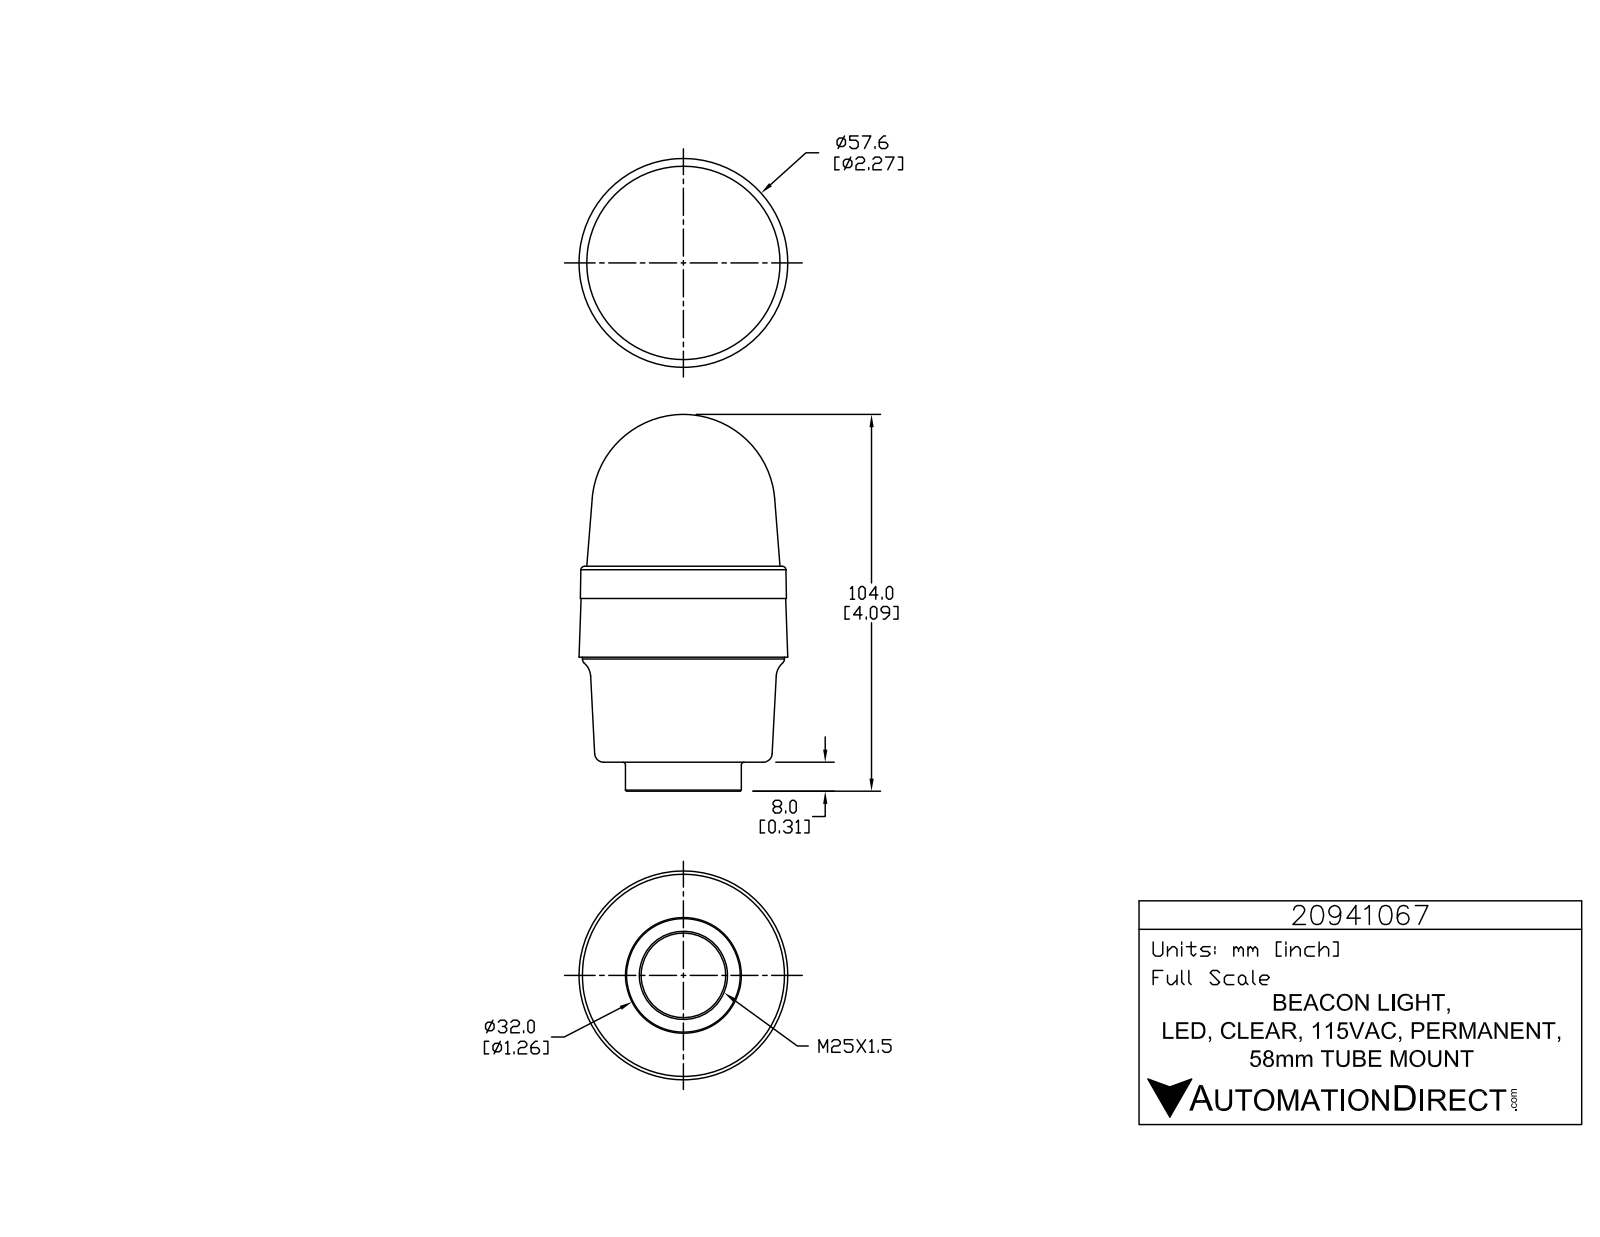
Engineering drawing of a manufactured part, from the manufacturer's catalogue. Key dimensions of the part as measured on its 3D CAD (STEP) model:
Part name (STEP PRODUCT): 20941067
STEP written by: SolidWorks 2015 (AUTOMOTIVE_DESIGN)
Units: inches
Bodies: 1 solid, 791 faces (525 planar, 168 cylindrical, 98 other)
Overall size (bounding box): 4.051 × 2.269 × 2.269
Volume: 11.72 in³ · Surface area: 29.93 in²
Round holes (diameter × count): ⌀0.039 ×3, ⌀0.92 ×1
Round bosses / shafts (diameter × count): ⌀0.226 ×3, ⌀0.056 ×3, ⌀2.197 ×1, ⌀1.26 ×1
Partial cylindrical surfaces — rounded edges, fillets, slot ends (radius × count): R0.008 ×6, R0.008 ×6, R0.008 ×6, R0.131 ×6, R0.004 ×3, R0.005 ×3, R0.008 ×3, R0.008 ×3
Main face-to-face distances: 0.315, 1.142, 1.457, 0.988, 2.13, 2.445, 0.35, 0.638, 1.78, 2.094
